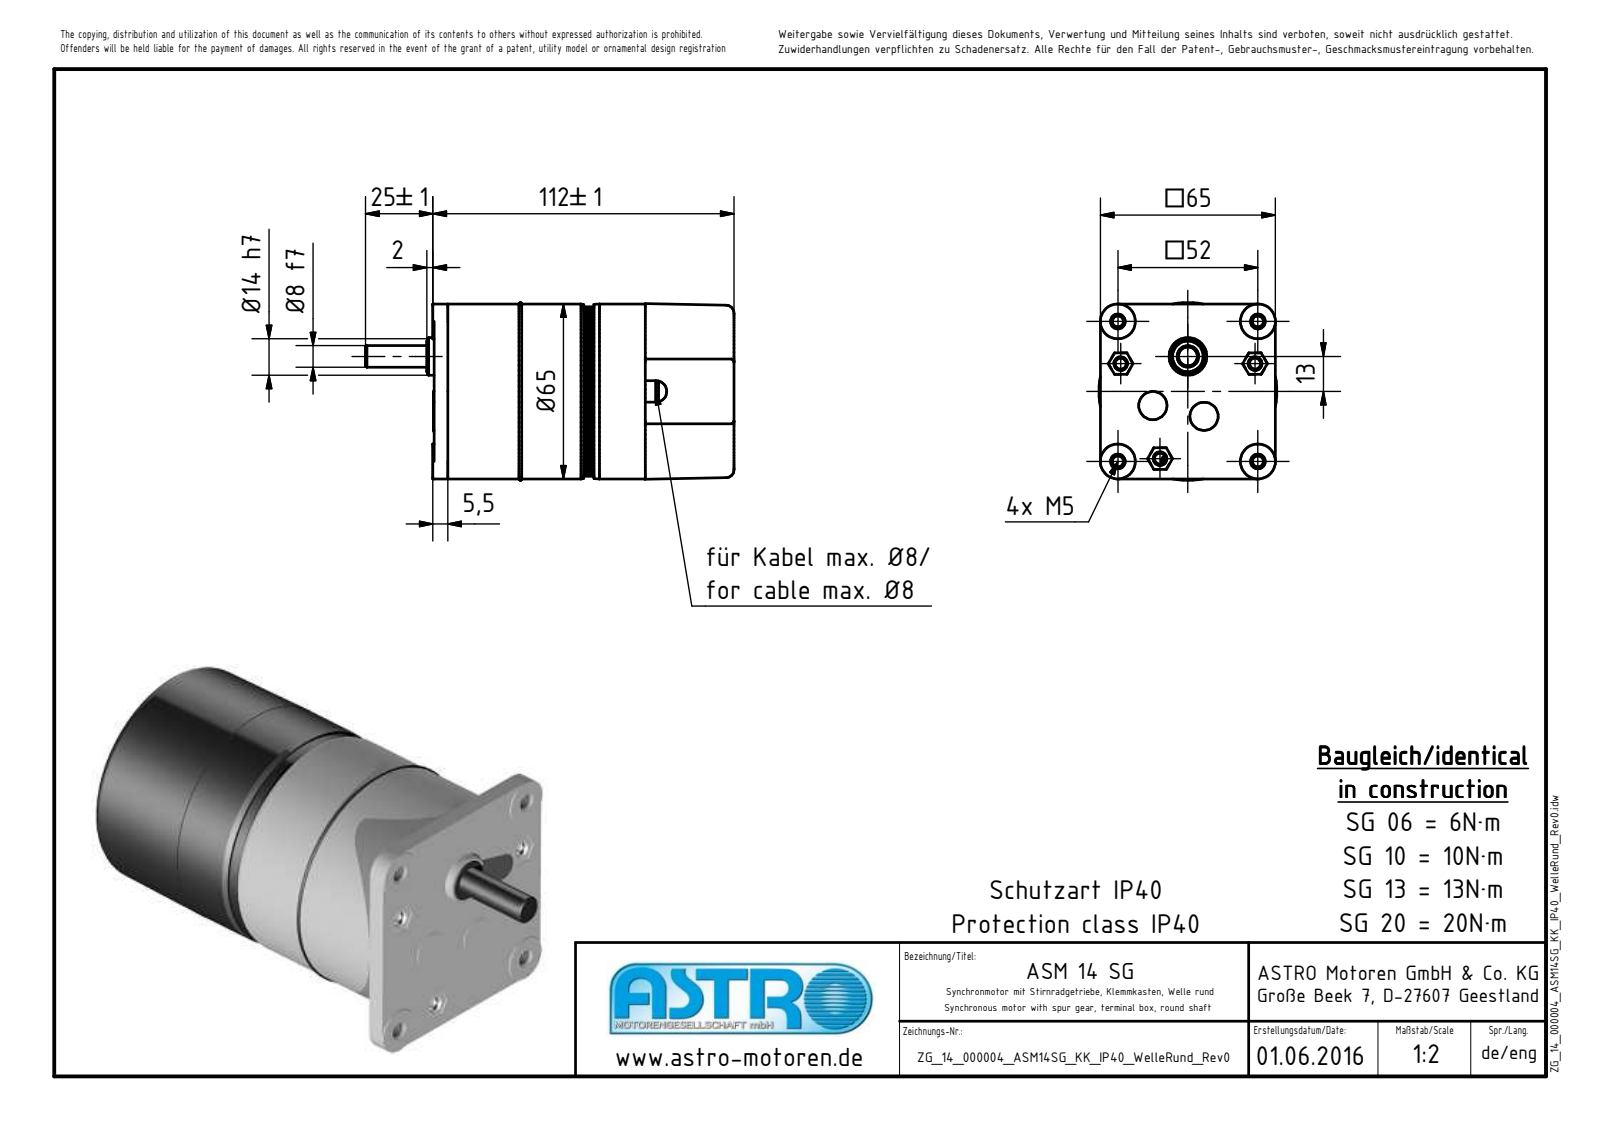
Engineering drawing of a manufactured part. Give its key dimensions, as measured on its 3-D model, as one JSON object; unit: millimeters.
{"part_name": "ZG_14_000024_ASM14SG_KK_IP40_WelleRund_Rev0; 5101-STG-Kunst; LagerschaleB3-ZG-Rev1-0; ZG_51108x067_Endwelle_8x67_Rev0 (+6 more)", "step_written_by": "Autodesk Inventor 2010 (AUTOMOTIVE_DESIGN)", "units": "millimeters", "bodies": {"solids": 14, "faces": 456, "planar": 183, "cylindrical": 87, "other": 186}, "overall_size": [137.1, 65.38, 65.38], "volume_mm3": 146710, "surface_area_mm2": 84312, "round_holes": [[4.1, 8], [5.2, 3], [4.3, 1], [6, 1], [8, 1], [8.5, 1], [12, 1], [15.5, 1], [16, 1], [59, 1], [63, 1]], "round_bosses_or_shafts": [[13, 4], [4, 4], [3.62, 4], [12.01, 2], [10.5, 2], [8.5, 2], [3, 2], [2.5, 2]], "partial_cylinders_radius": [[0.5, 16], [1, 5], [5.26, 4], [4, 1]], "face_to_face_distances": [44.8, 77.6, 54.3, 9.5, 7, 51.8, 61.3, 70.6, 25.8, 16.3], "hole_center_spacings": [27, 49.89, 20.66, 38.18, 44.9, 52.96, 10.53, 10.54]}
